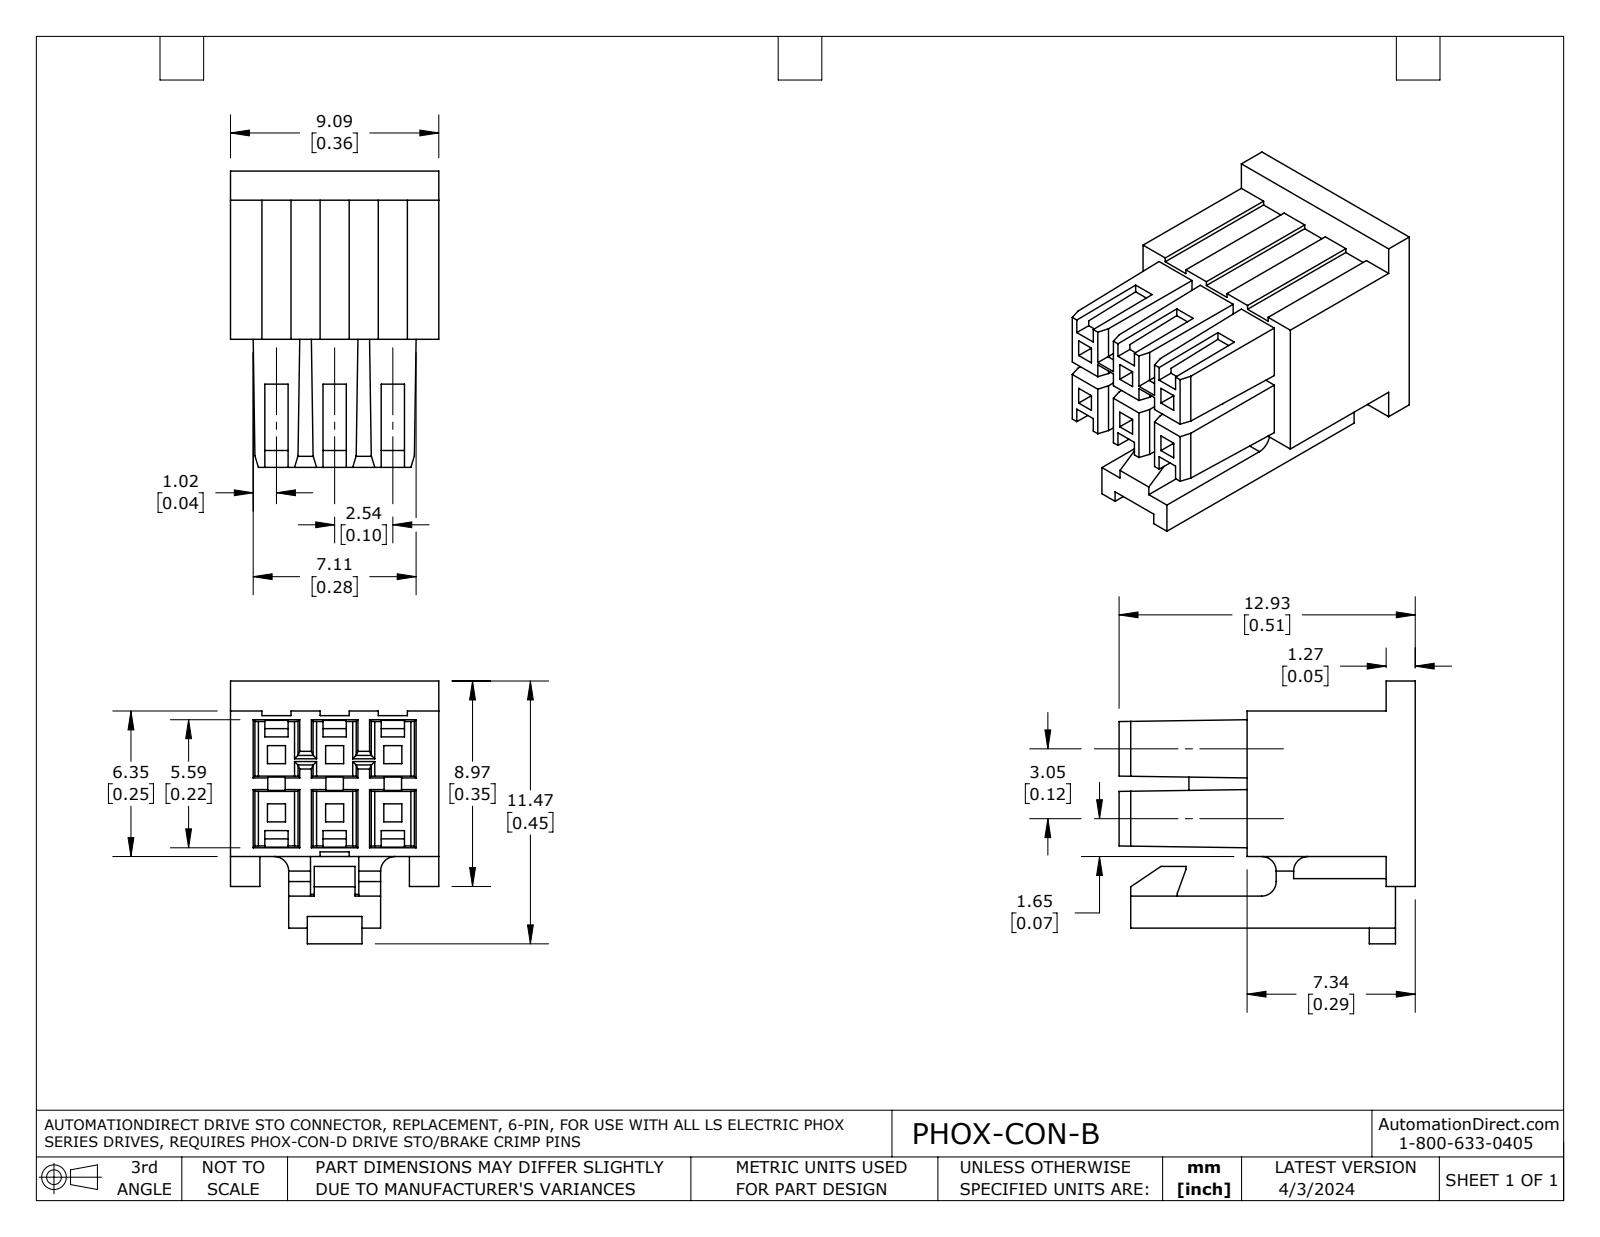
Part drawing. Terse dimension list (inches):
name: PHOX-CON-B
written by: SolidWorks 2021 (AUTOMOTIVE_DESIGN)
unit: in
bodies: 1 solid, 278 faces (270 planar, 8 cylindrical, 0 other)
size: 0.509 × 0.451 × 0.358
volume: 0.024 in³; area: 2.165 in²
rounds: 5× R0.025
face distances: 0.1, 0.2, 0.15, 0.25, 0.103, 0.12, 0.067, 0.05, 0.109, 0.209
